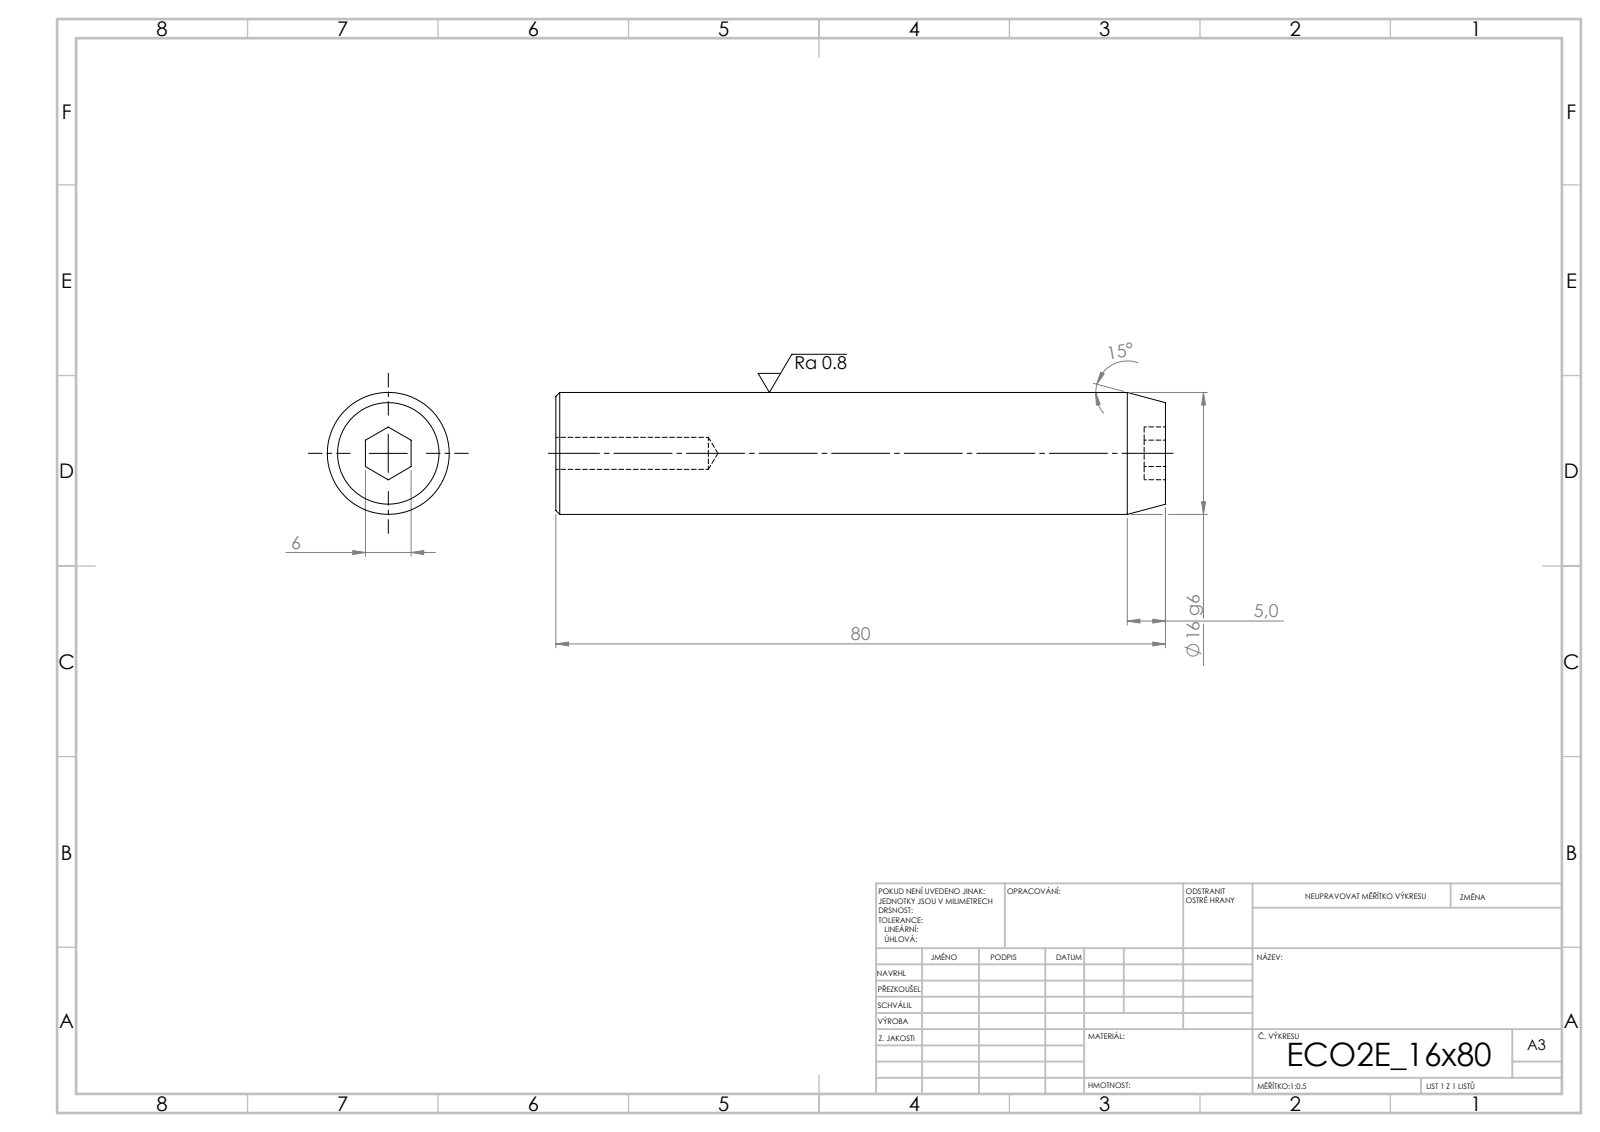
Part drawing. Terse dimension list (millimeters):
written by: SolidWorks 2019 (CONFIG_CONTROL_DESIGN)
unit: mm
bodies: 1 solid, 19 faces (9 planar, 4 cylindrical, 6 other)
size: 80 × 16 × 16
volume: 15 550 mm³; area: 4 658 mm²
holes: 1× ⌀4.2
bosses: 1× ⌀16
face distances: 80, 2.8, 77.2, 6
